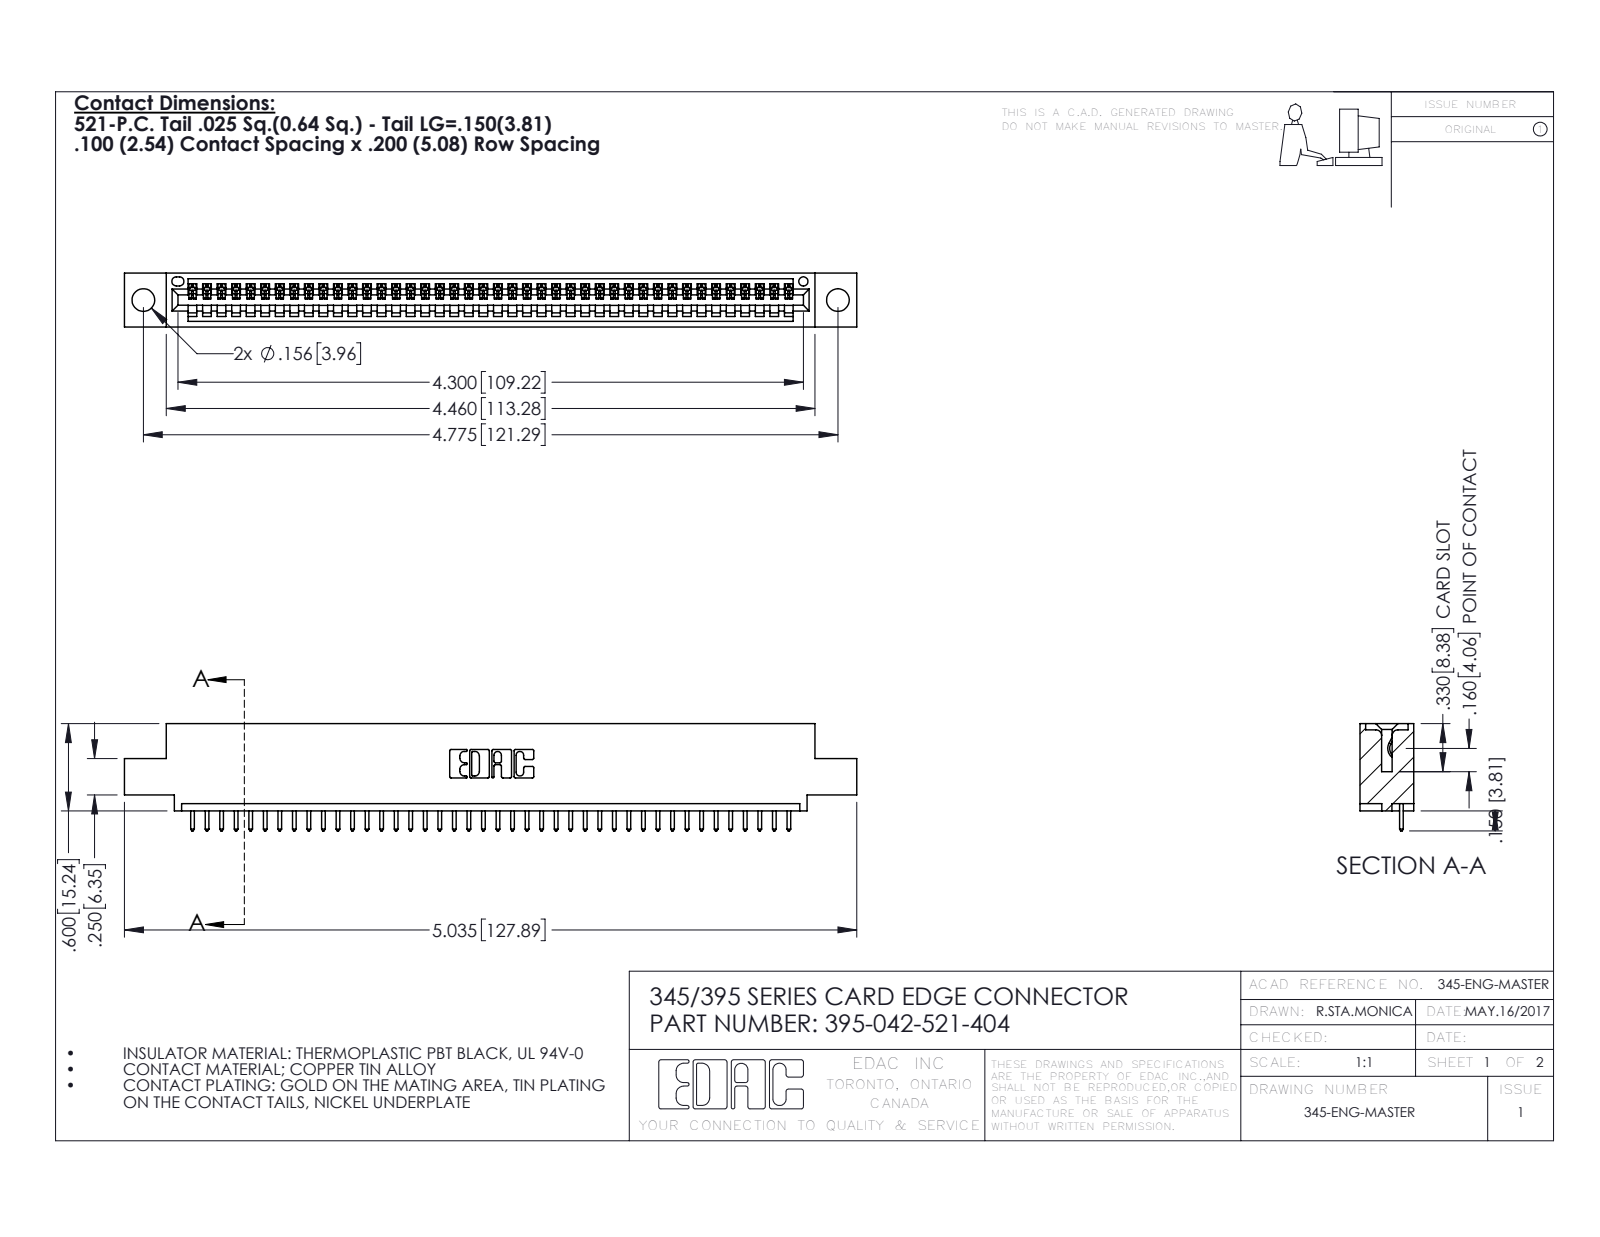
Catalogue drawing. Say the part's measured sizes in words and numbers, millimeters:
The part is named "345-292-001_345-293-121; 395-042-521-404; 345 Part_0.110 Offset - 0.156 Dia-TH". Its 3-D file was written by "SolidWorks 2016 (CONFIG_CONTROL_DESIGN)". It is 43 solids with 2566 faces: 1764 planar, 802 cylindrical and 0 other. Overall it measures 127.9 by 18.7 by 9.4 millimeters. Its volume is 11 900 cubic millimeters and its surface area 15 190 square millimeters. Round holes: 2 of diameter 4, 1 of diameter 1.6. Partial cylindrical surfaces (rounded edges, fillets, slot ends): 84 of radius 0.2, 84 of radius 0.3, 22 of radius 0.3, 6 of radius 0.2, 6 of radius 0.8, 3 of radius 0.7, 2 of radius 0.8, 2 of radius 1. The main face-to-face distances are 7.6, 1.8, 9.4, 5.1, 2.5, 6.9, 0.6, 5.7, 3.8, 1.8. The hole center spacings are 6.9, 115.3, 121.3.
